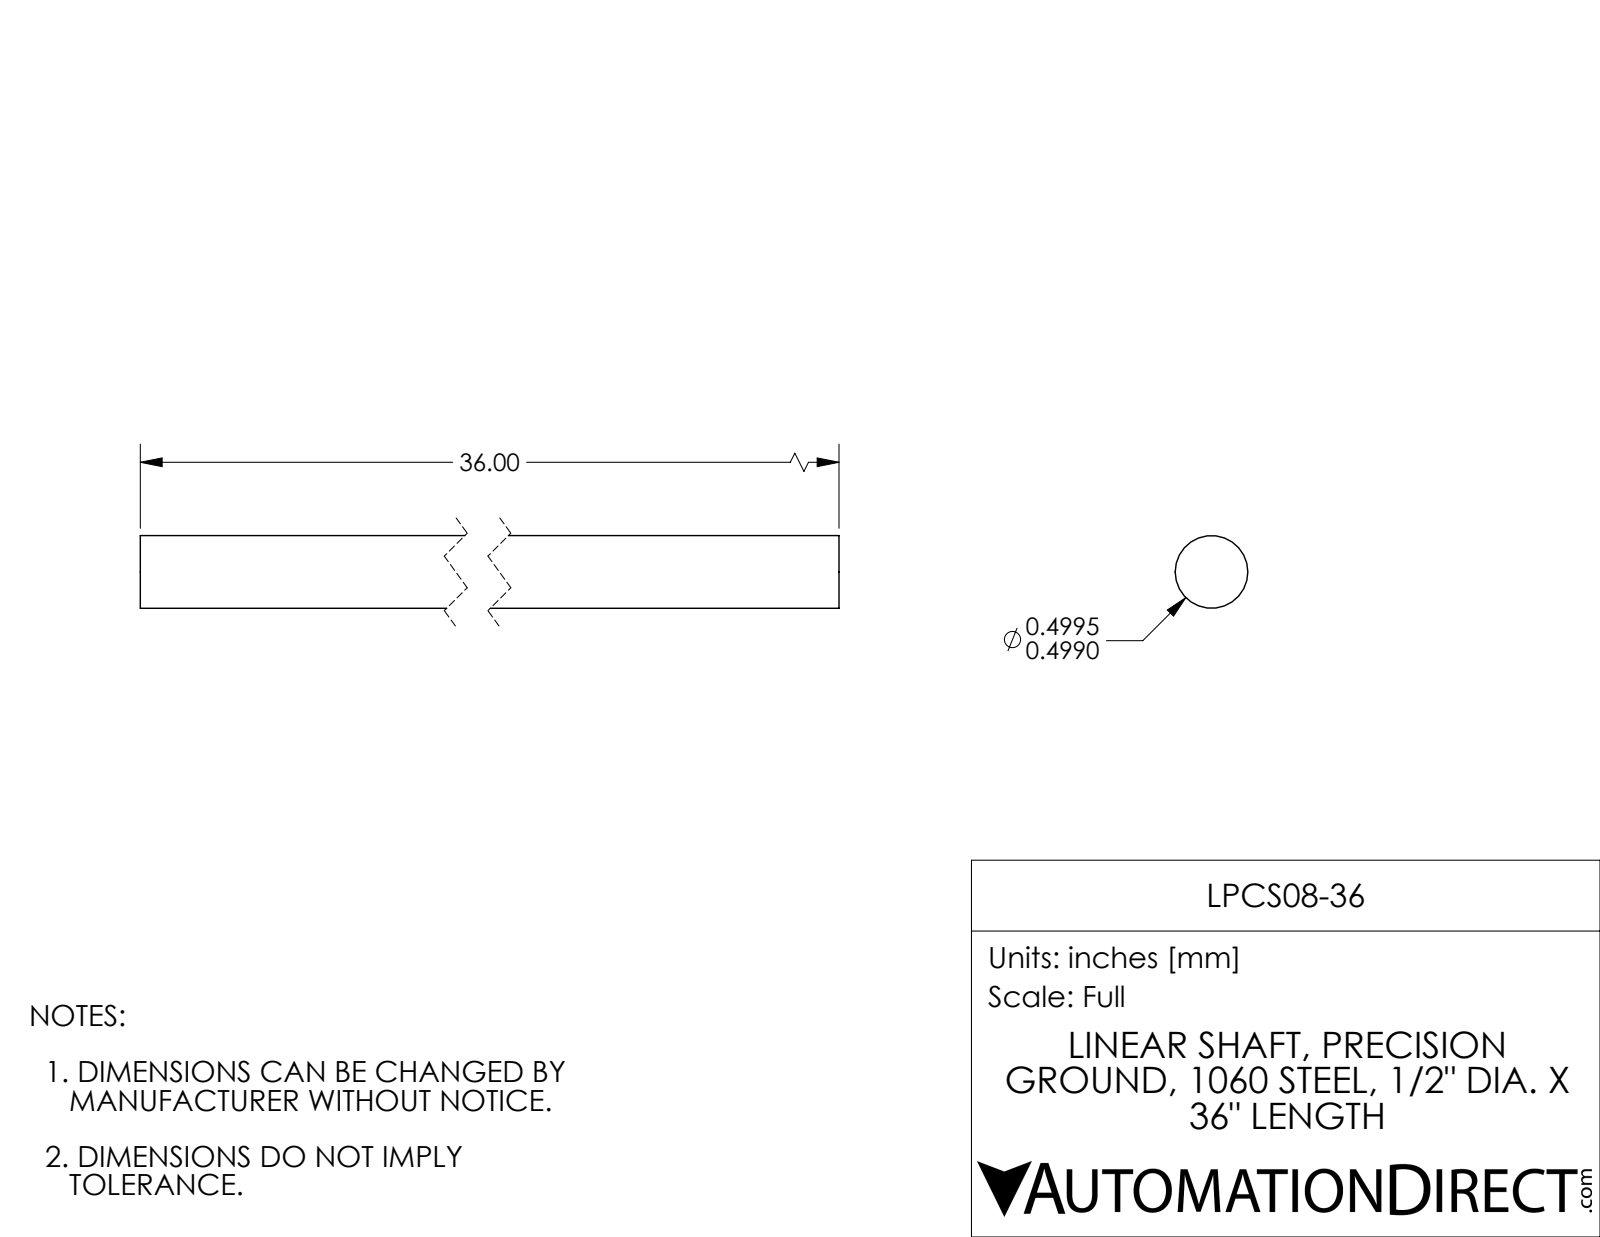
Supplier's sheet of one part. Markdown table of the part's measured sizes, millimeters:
| quantity | value |
| --- | --- |
| part name | LPCS08-36 |
| STEP written by | SolidWorks 2017 (AUTOMOTIVE_DESIGN) |
| units | millimeters |
| bodies | 1 solid, 4 faces (2 planar, 2 cylindrical, 0 other) |
| overall size | 914.4 × 12.7 × 12.7 |
| volume | 115 600 mm³ |
| surface area | 36 700 mm² |
| round bosses / shafts (diameter × count) | 12.7 × 1 |
| main face-to-face distances | 914.4 |
